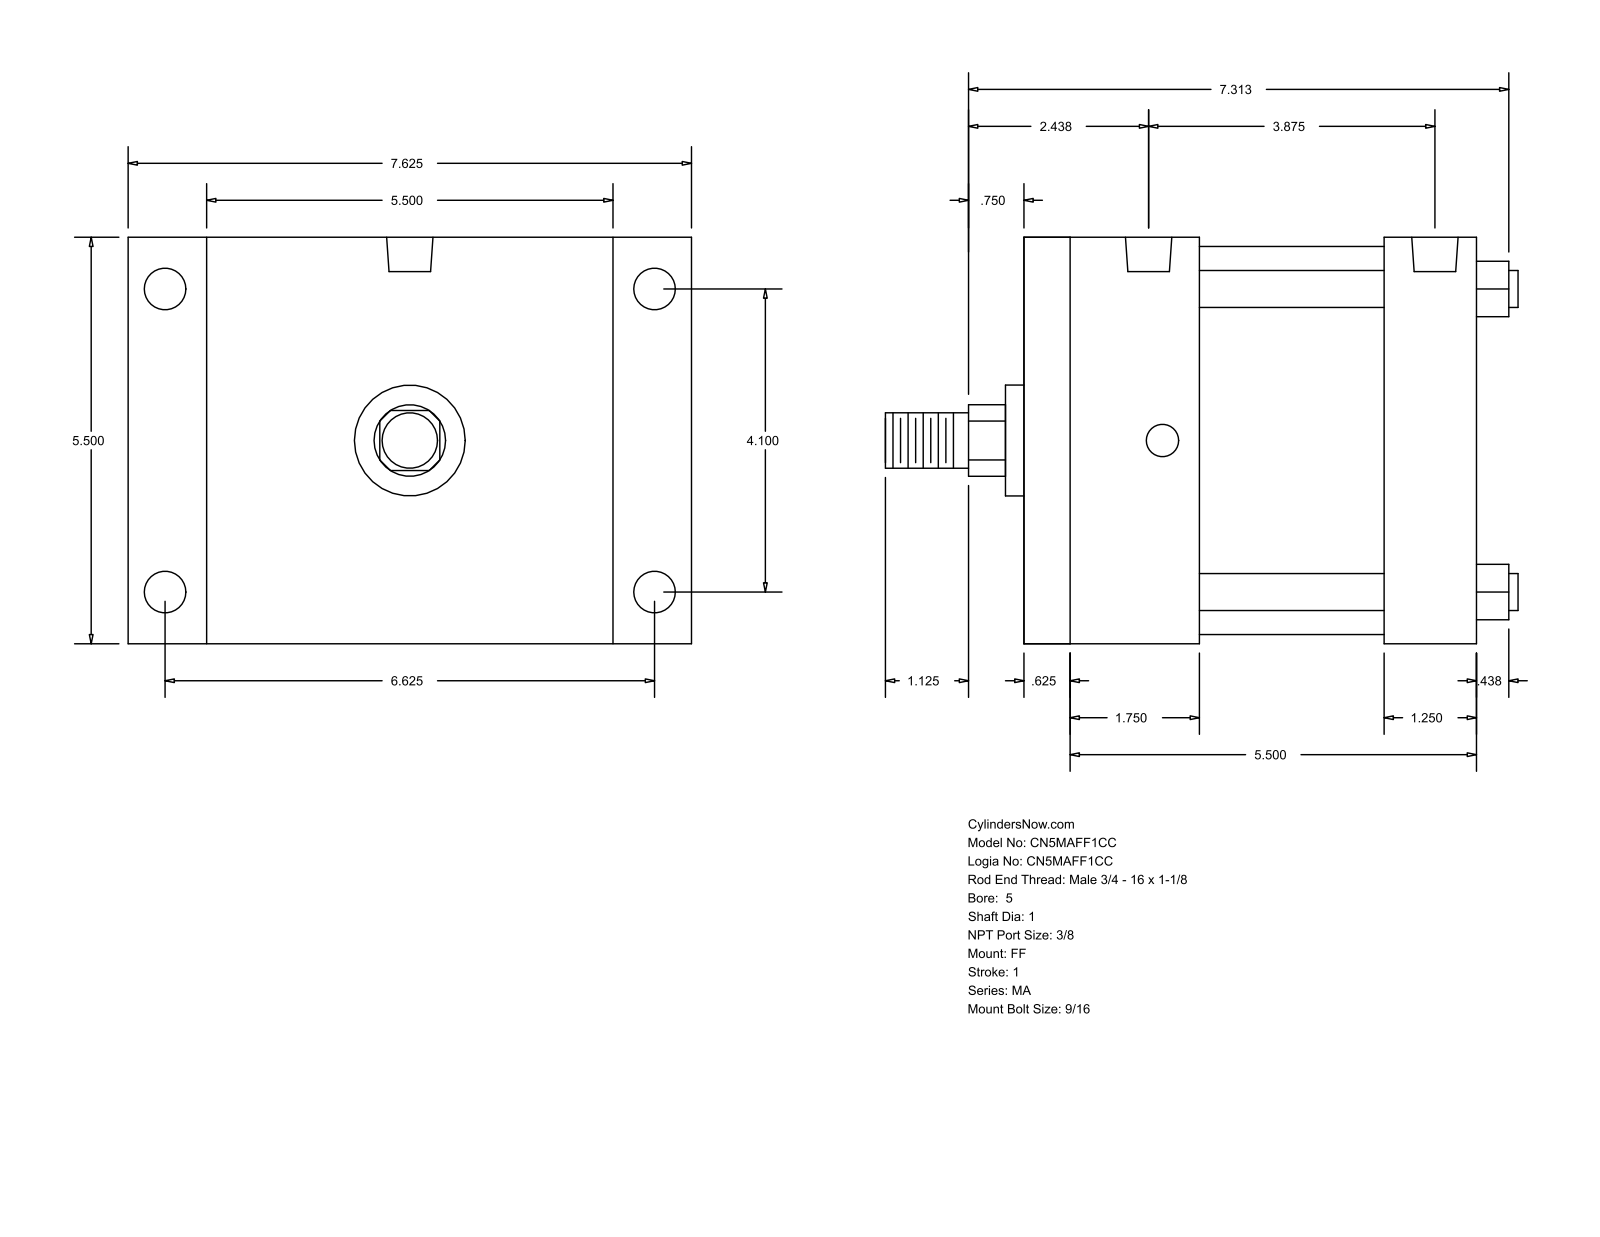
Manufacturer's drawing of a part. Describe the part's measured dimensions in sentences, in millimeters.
The part is named "MA_FF__0500_1". Its 3-D file was written by "GSSL Pune (CONFIG_CONTROL_DESIGN)". It is 0 solids with 92 faces: 64 planar, 28 cylindrical and 0 other. Overall it measures 217.49 by 193.68 by 139.7 millimeters. Round holes: 4 of diameter 11.11, 4 of diameter 14.29, 2 of diameter 15.93. Round bosses or shafts: 4 of diameter 12.7, 1 of diameter 133.35, 1 of diameter 38.1, 1 of diameter 25.4, 1 of diameter 19.05. Partial cylindrical surfaces (rounded edges, fillets, slot ends): 1 of radius 12.29. The main face-to-face distances are 139.7, 155.57, 15.87, 166.69, 123.83, 107.96, 31.74, 60.33, 44.46, 63.5. The hole center spacings are 88.9, 104.14, 168.28, 197.9, 4.76, 4.77, 93.66, 93.67.
